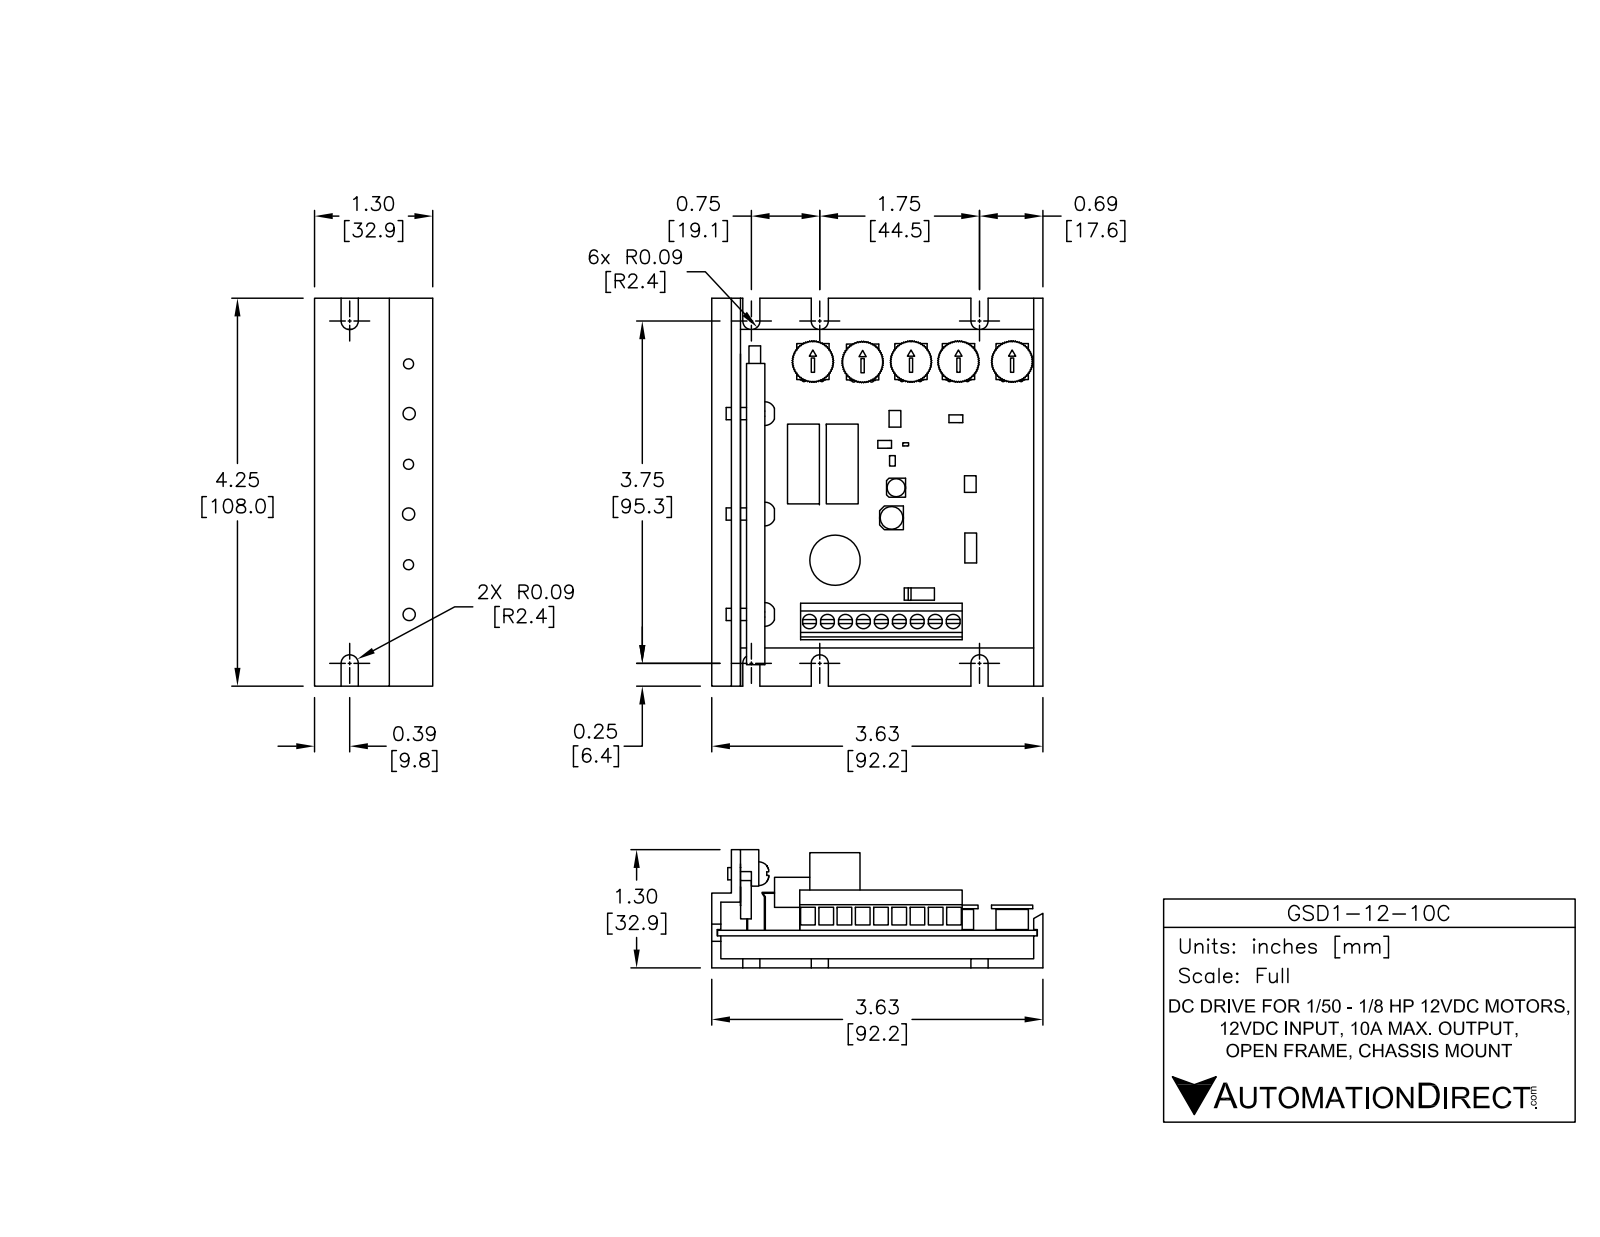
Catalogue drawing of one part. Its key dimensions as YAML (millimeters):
part_name: "CAPR500-1250x4000; C19; HDS6P7; HDM9 (+8 more)"
step_written_by: "SolidWorks 2014 (AUTOMOTIVE_DESIGN)"
units: millimeters
bodies: {solids: 334, faces: 4776, planar: 3404, cylindrical: 1125, other: 247}
overall_size: [108, 91.9, 51.5]
volume: 90470
surface_area: 75100
round_holes:
  - {diameter: 0.8, count: 35}
  - {diameter: 1, count: 18}
  - {diameter: 1.2, count: 15}
  - {diameter: 0.3, count: 10}
  - {diameter: 4, count: 9}
  - {diameter: 1.1, count: 8}
  - {diameter: 0.9, count: 6}
  - {diameter: 1.3, count: 5}
  - {diameter: 2.6, count: 5}
  - {diameter: 3.8, count: 5}
  - {diameter: 1.5, count: 4}
  - {diameter: 1, count: 3}
round_bosses_or_shafts:
  - {diameter: 0.6, count: 18}
  - {diameter: 0.6, count: 18}
  - {diameter: 0.5, count: 15}
  - {diameter: 1, count: 11}
  - {diameter: 1.7, count: 8}
  - {diameter: 1.3, count: 8}
  - {diameter: 0.6, count: 4}
  - {diameter: 3.4, count: 3}
partial_cylinders:
  - {radius: 0.1, count: 32}
  - {radius: 0.1, count: 28}
  - {radius: 0.1, count: 24}
  - {radius: 0.6, count: 11}
  - {radius: 2.4, count: 8}
  - {radius: 0.1, count: 4}
  - {radius: 0.2, count: 4}
  - {radius: 0.3, count: 4}
face_to_face_distances: [3.6, 6.4, 1.6, 7.9, 11.5, 9.9, 3.8, 5.1, 83.1, 8.9]
hole_center_spacings: [26.8, 2.5, 7.9, 10.3, 13.3, 13.3, 13.6, 14]
